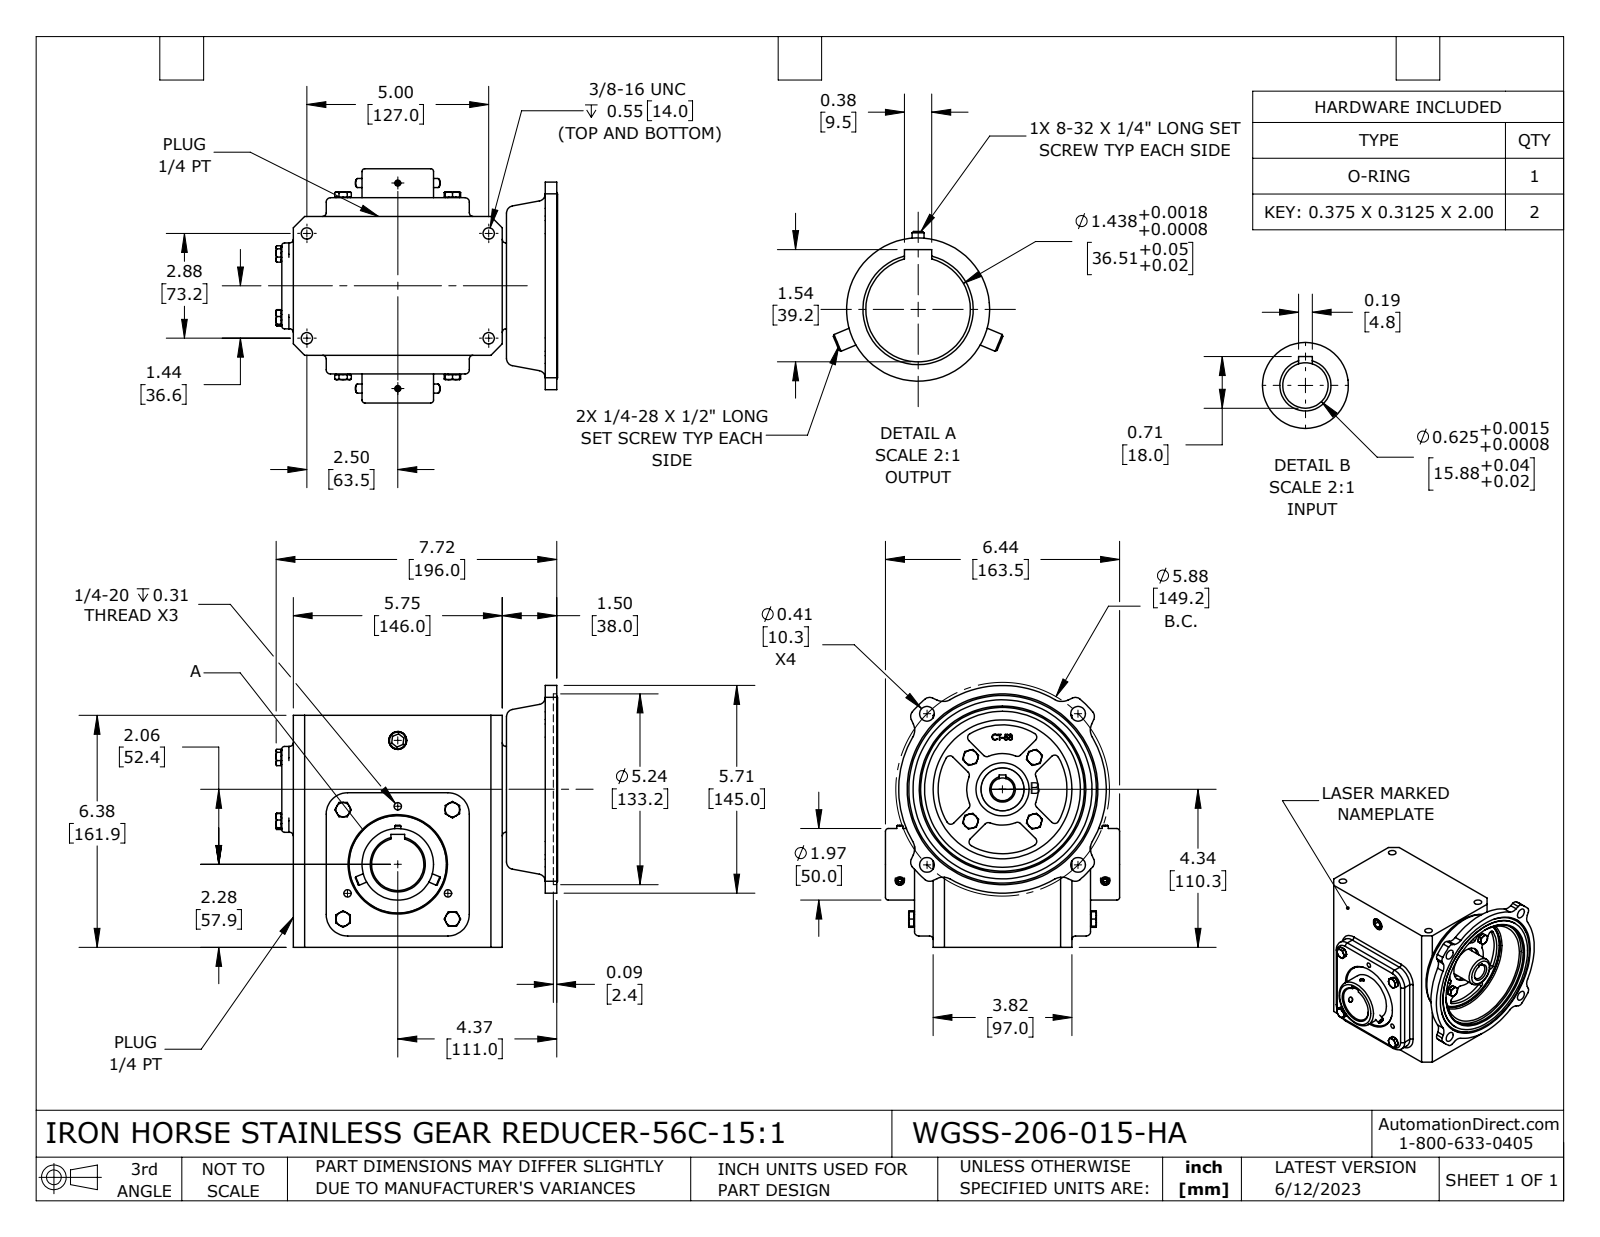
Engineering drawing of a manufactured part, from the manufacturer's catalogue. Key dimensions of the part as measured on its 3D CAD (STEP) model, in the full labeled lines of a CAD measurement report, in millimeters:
Part name (STEP PRODUCT): WGSS-206-015-HA
STEP written by: SolidWorks 2021 (CONFIG_CONTROL_DESIGN)
Units: millimetres
Bodies: 7 solids, 895 faces (396 planar, 235 cylindrical, 264 other)
Overall size (bounding box): 196.6 × 182.8 × 163.5
Volume: 2 617 000 mm³ · Surface area: 208 800 mm²
Round holes (diameter × count): ⌀5.4 ×4, ⌀8 ×4, ⌀10.3 ×4, ⌀5.1 ×3, ⌀3.5 ×2, ⌀15.9 ×1, ⌀22 ×1, ⌀36.5 ×1, ⌀36.6 ×1, ⌀37 ×1, ⌀40 ×1, ⌀97 ×1
Round bosses / shafts (diameter × count): ⌀10 ×8, ⌀6.4 ×4, ⌀4.2 ×2, ⌀125 ×1, ⌀68 ×1, ⌀50 ×1, ⌀30 ×1
Partial cylindrical surfaces — rounded edges, fillets, slot ends (radius × count): R3 ×24, R2.5 ×16, R10 ×12, R5 ×8, R2 ×4, R8 ×4, R15 ×4, R25 ×1
Main face-to-face distances: 161.9, 97, 13, 110, 146, 3, 8, 184, 123, 4
Hole centre spacings: 72.6, 74.6, 105.5, 125.6, 40.5, 143.5, 70.2, 73.2
